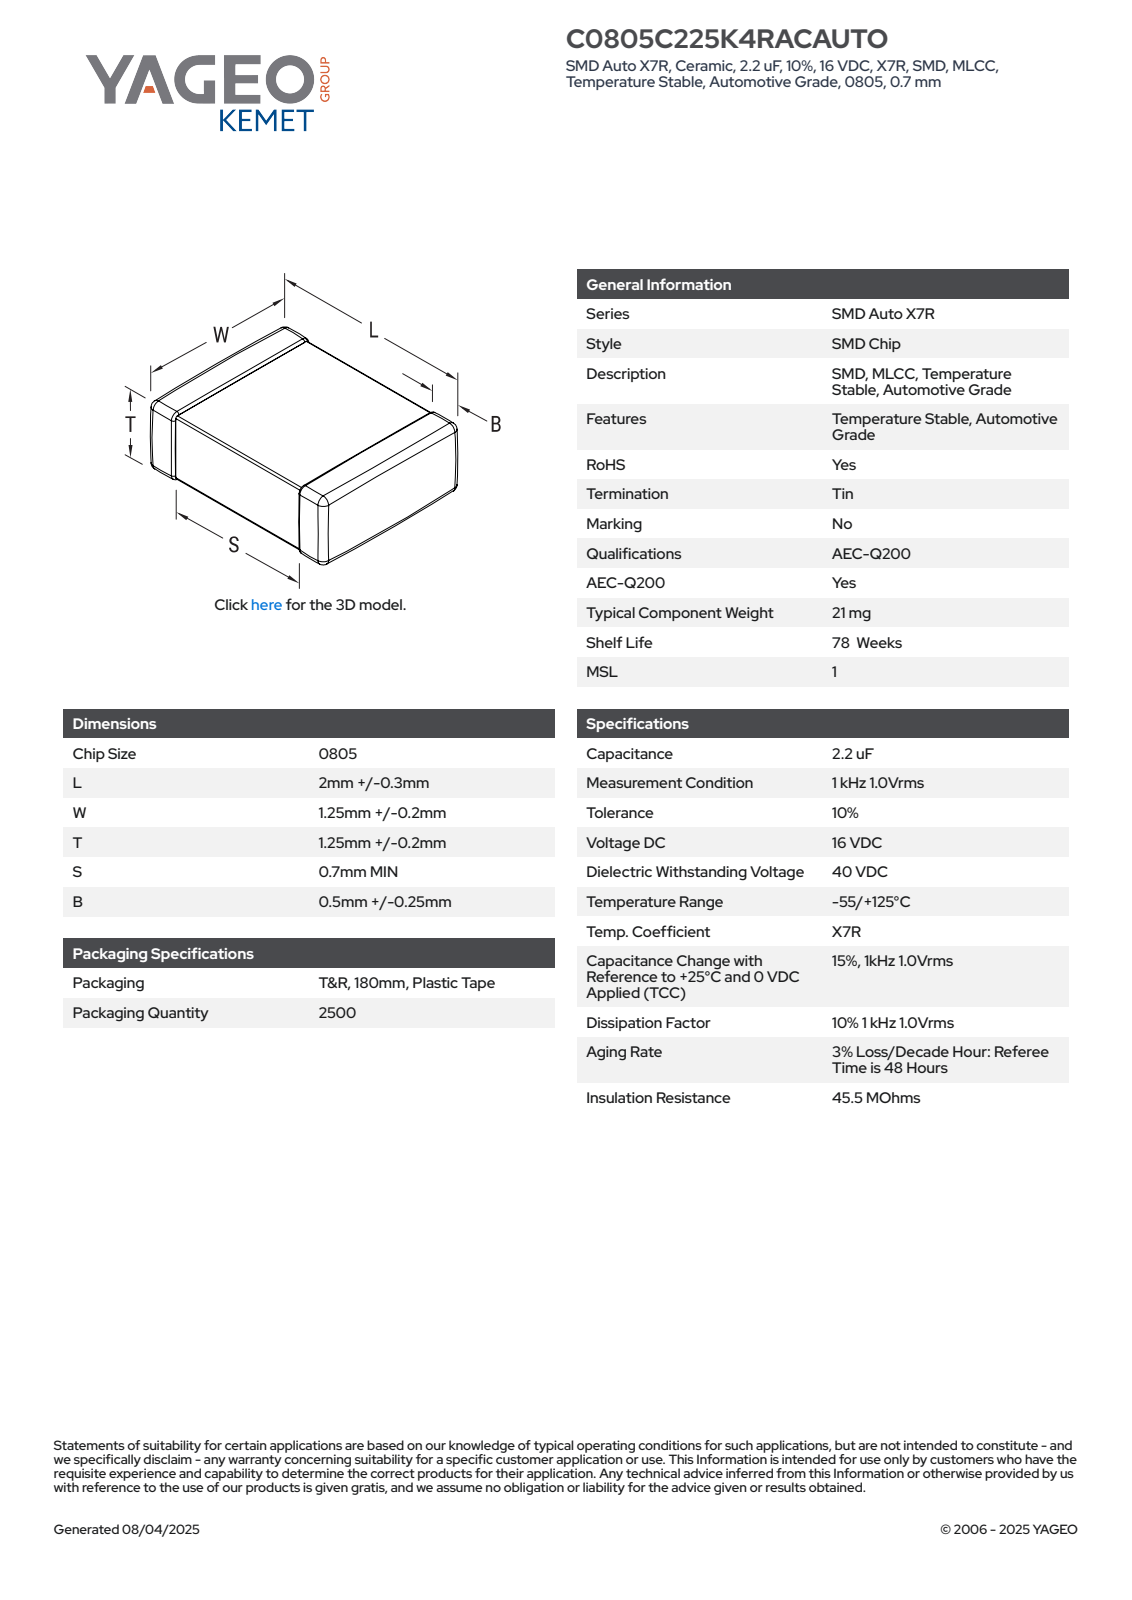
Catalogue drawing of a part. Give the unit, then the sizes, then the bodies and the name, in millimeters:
Units: millimetres
Overall size (bounding box): 2.3 × 1.45 × 1.45
Main face-to-face distances: 1.42, 1.45, 1.39, 2.3, 1.03, 1.27, 1.24, 1.06, 1.15, 0.87
Volume: 5 mm³ · Surface area: 18 mm²
Bodies: 4 solids, 125 faces (71 planar, 38 cylindrical, 16 other)
Part name (STEP PRODUCT): CCS_CCSTD_0805_L2.3W1.45T1.45S0.7B0.75
STEP written by: SolidWorks 2021 (AUTOMOTIVE_DESIGN)
